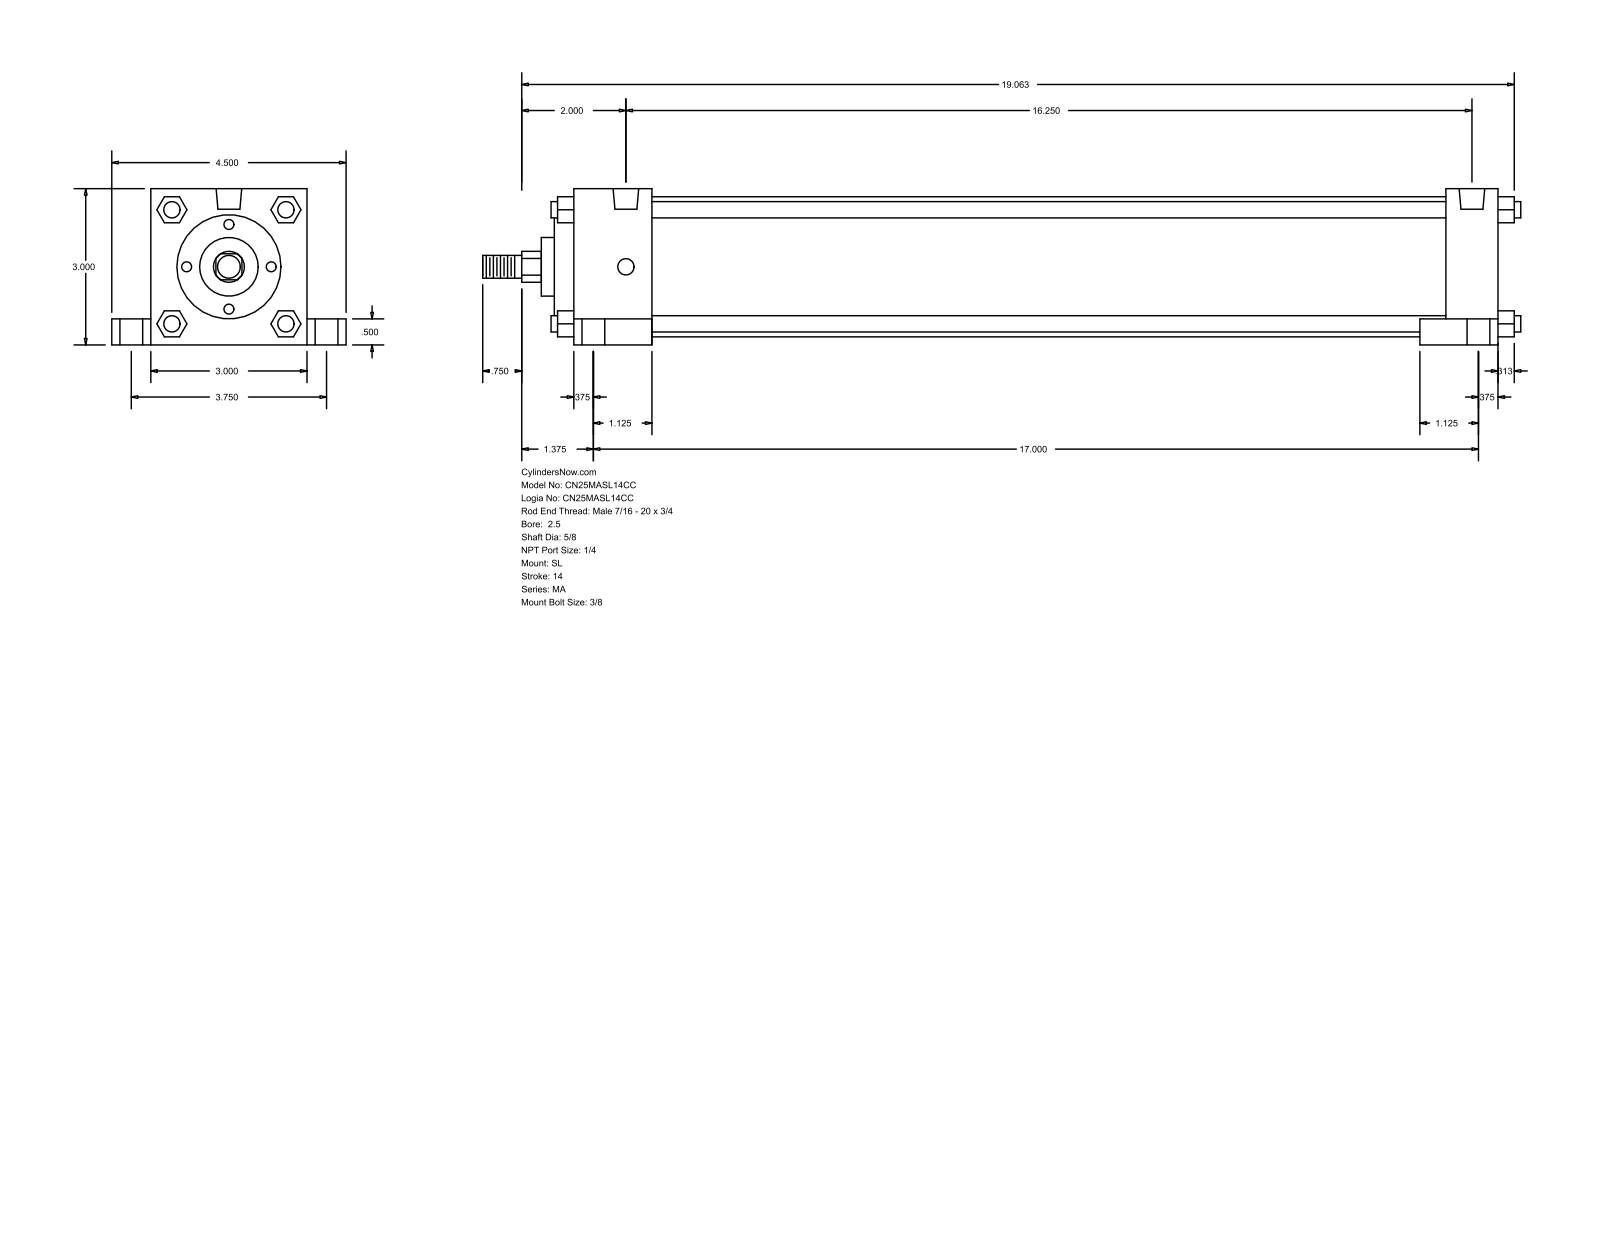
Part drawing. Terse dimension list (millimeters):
name: MA_SL__0250_0.625
written by: GSSL Pune (CONFIG_CONTROL_DESIGN)
unit: mm
bodies: 0 solids, 150 faces (113 planar, 37 cylindrical, 0 other)
size: 506.41 × 114.3 × 76.2
holes: 4× ⌀7.94, 4× ⌀11.11, 4× ⌀17.46, 2× ⌀12.49
bosses: 4× ⌀7.94, 1× ⌀68.33, 1× ⌀50.8, 1× ⌀28.57, 1× ⌀15.88, 1× ⌀11.11
rounds: 1× R7.54
face distances: 76.2, 450.85, 12.7, 387.35, 25.4, 38.1, 412.75, 425.45, 19.05, 63.5
hole spacings: 47.73, 50.2, 95.24, 412.75, 418.65, 431.27, 431.81, 442.19
